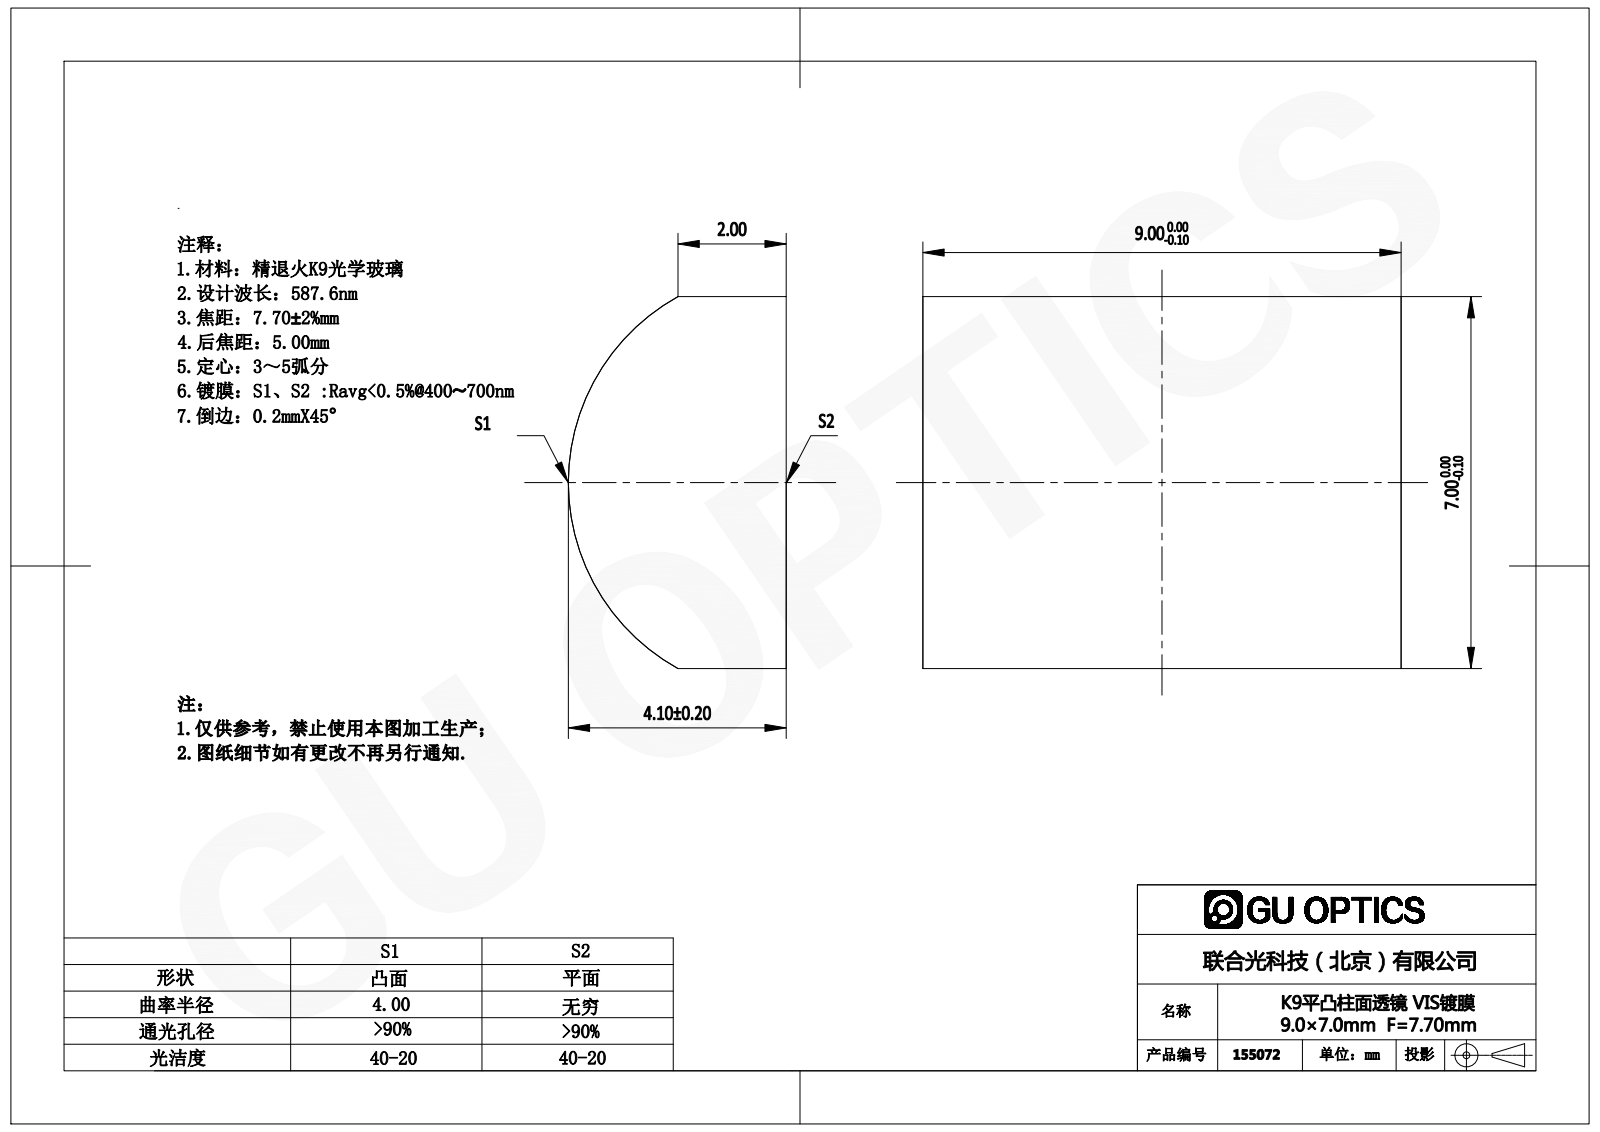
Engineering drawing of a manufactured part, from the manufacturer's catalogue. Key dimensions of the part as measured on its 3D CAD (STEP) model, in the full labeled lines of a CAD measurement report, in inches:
Part name (STEP PRODUCT): 155006
STEP written by: SolidWorks 2016 (AUTOMOTIVE_DESIGN)
Units: inches
Bodies: 1 solid, 6 faces (5 planar, 1 cylindrical, 0 other)
Overall size (bounding box): 0.354 × 0.276 × 0.161
Volume: 0.013 in³ · Surface area: 0.349 in²
Partial cylindrical surfaces — rounded edges, fillets, slot ends (radius × count): R0.157 ×1
Main face-to-face distances: 0.354, 0.276
